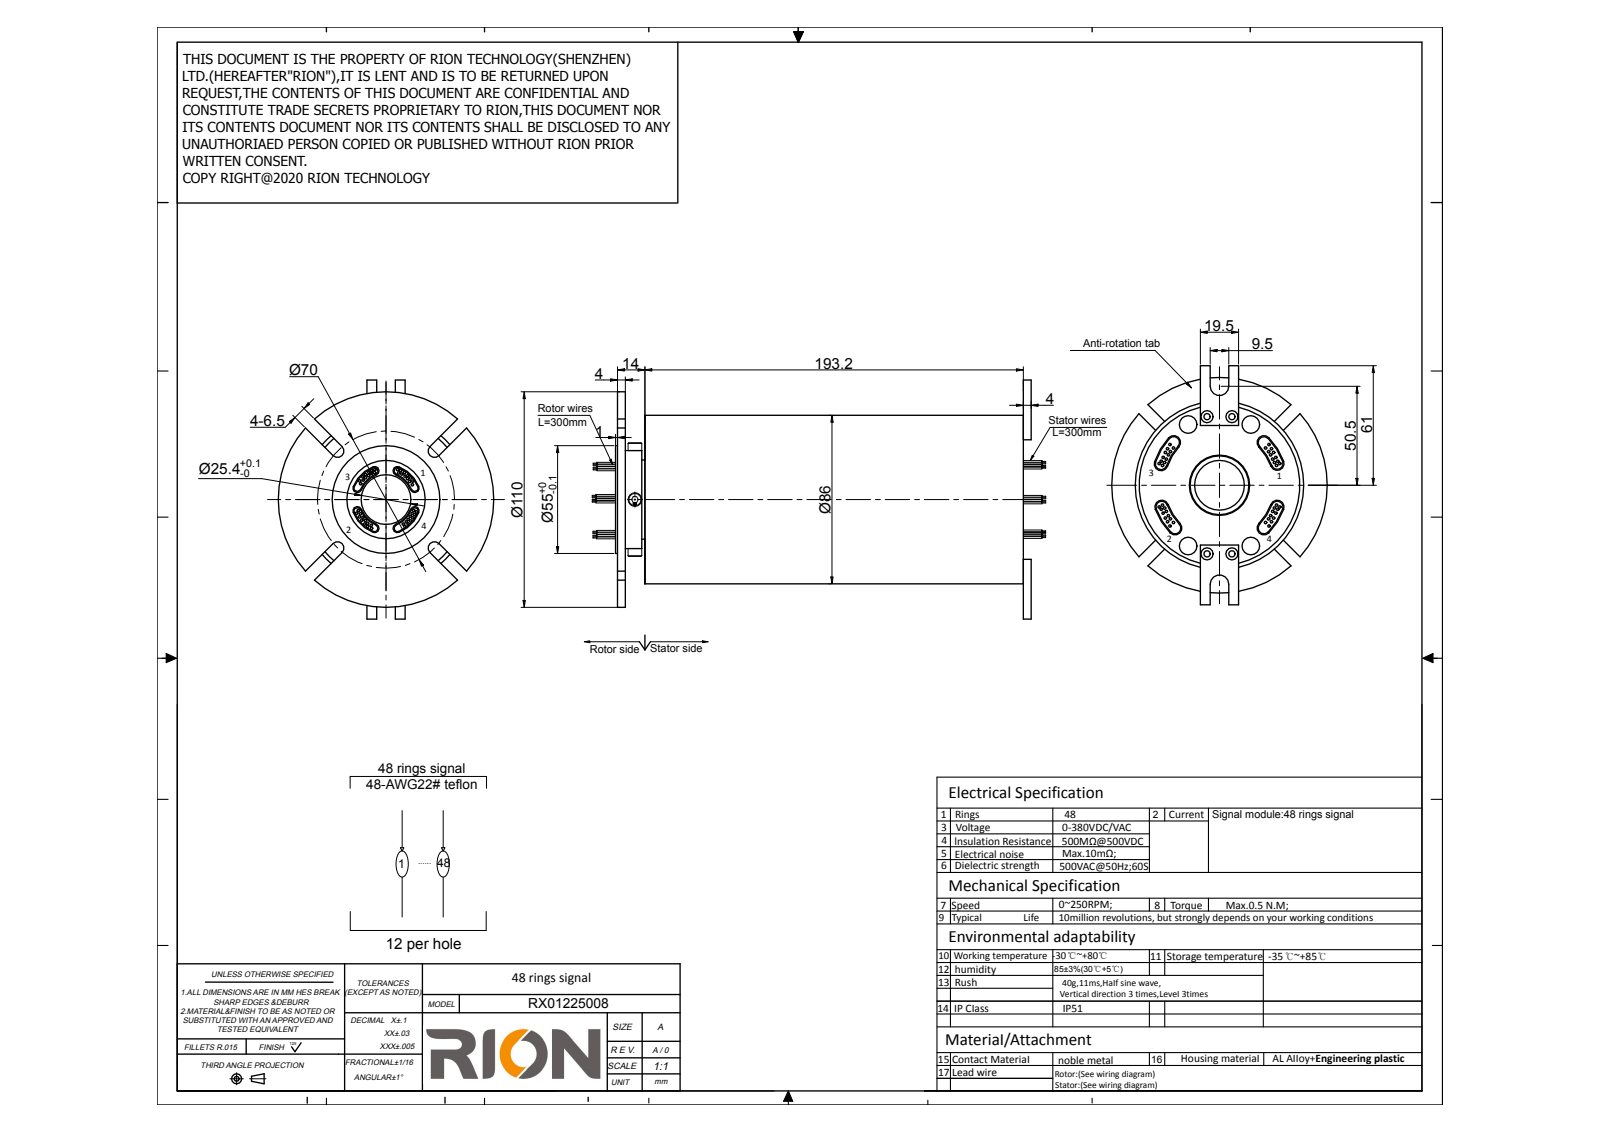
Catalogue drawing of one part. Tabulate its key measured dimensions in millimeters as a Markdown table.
| quantity | value |
| --- | --- |
| STEP written by | SolidWorks 2014 (CONFIG_CONTROL_DESIGN) |
| units | millimeters |
| bodies | 1 solid, 454 faces (158 planar, 280 cylindrical, 16 other) |
| overall size | 240.8 × 122 × 110 |
| volume | 1 078 000 mm³ |
| surface area | 113 216 mm² |
| round holes (diameter × count) | 2.5 × 4, 3.2 × 4, 25.4 × 1, 30.8 × 1, 46 × 1, 82 × 1 |
| round bosses / shafts (diameter × count) | 1.3 × 96, 110 × 1, 86 × 1, 81.8 × 1, 58 × 1, 55 × 1, 44 × 1, 30.4 × 1 |
| partial cylindrical surfaces (radius × count) | 2 × 16, 3.25 × 4, 4.75 × 2, 14 × 1, 18 × 1 |
| main face-to-face distances | 4, 207.2, 203.2, 14, 193.2, 10, 12.4, 8.4, 1.6, 194.8 |
| hole center spacings | 35.57, 12.7, 70, 71.14 |
